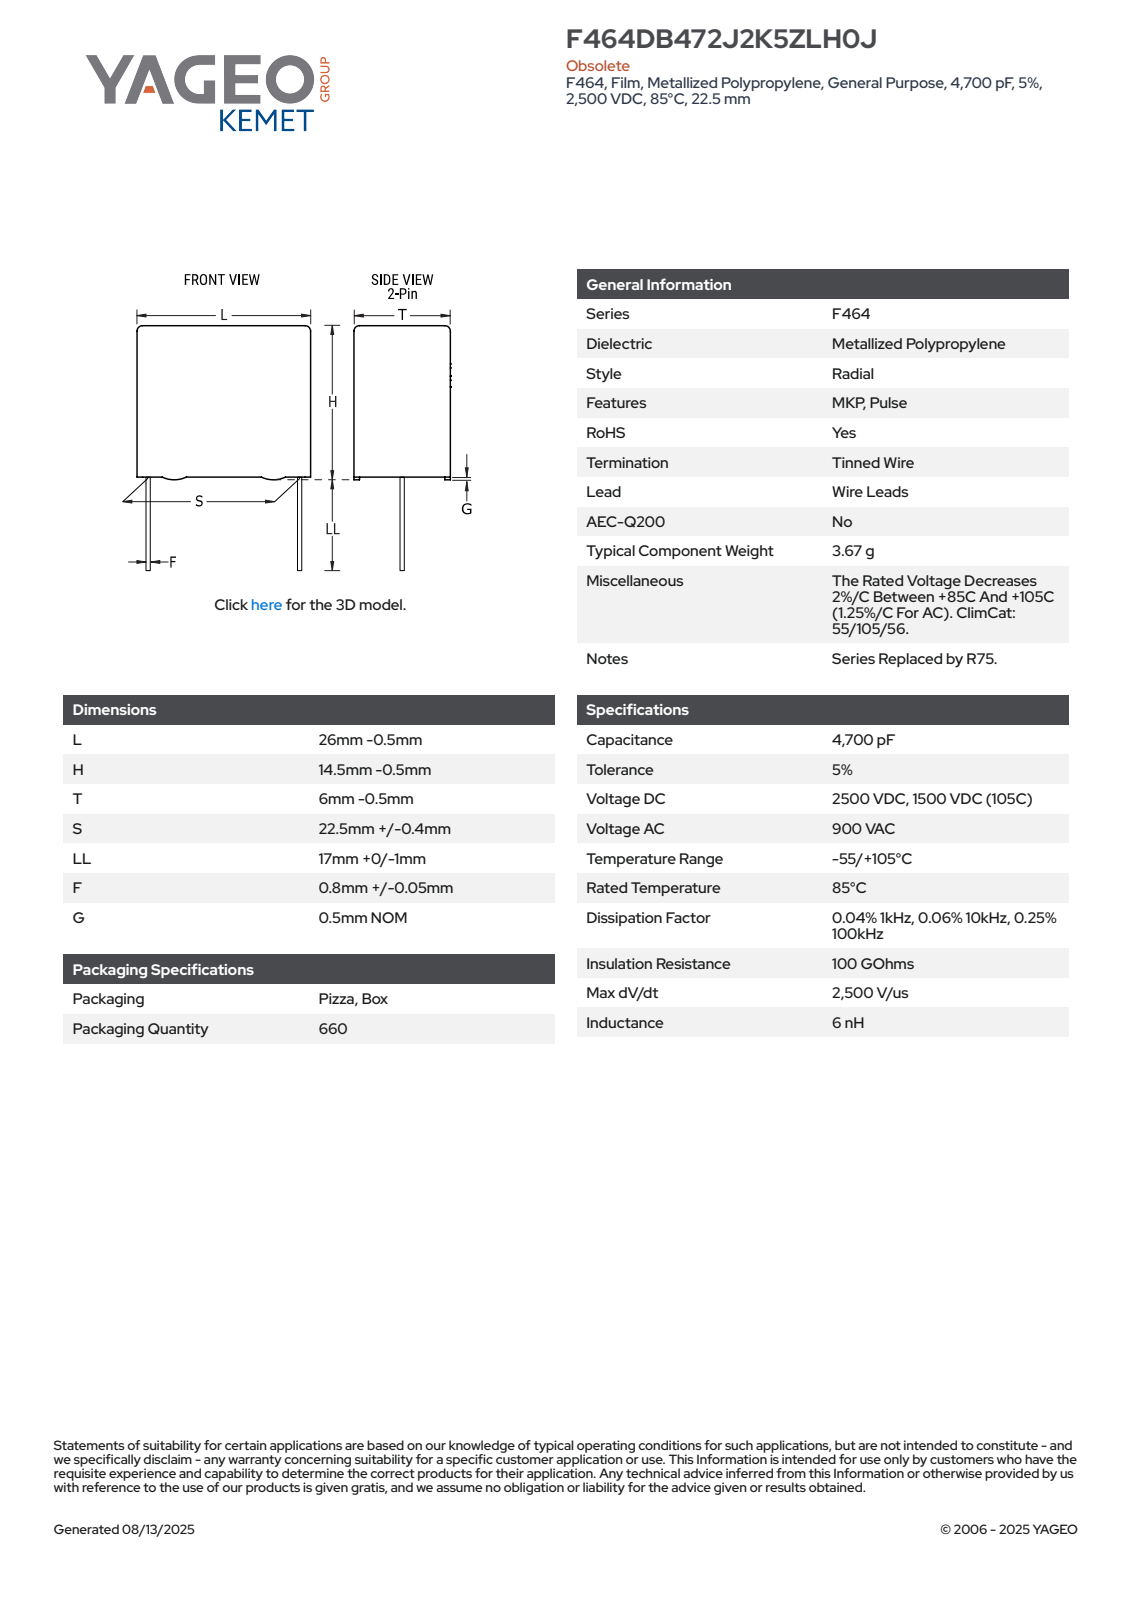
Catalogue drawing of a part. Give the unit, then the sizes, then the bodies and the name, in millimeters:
Units: millimetres
Overall size (bounding box): 31 × 25.5 × 5.5
Round bosses / shafts (diameter × count): ⌀0.85 ×2
Partial cylindrical surfaces — rounded edges, fillets, slot ends (radius × count): R0.5 ×4
Main face-to-face distances: 5.5, 13.5, 25.5, 0.31, 5.19, 0.5, 14, 4.88, 17, 17.5
Volume: 1 913 mm³ · Surface area: 1 285 mm²
Bodies: 4 solids, 89 faces (81 planar, 8 cylindrical, 0 other)
Part name (STEP PRODUCT): CFR_RBG_26X14.5X6_L25.5H14T5.5S22.5LL17F0.85G0.5
STEP written by: SolidWorks 2014 (AUTOMOTIVE_DESIGN)
